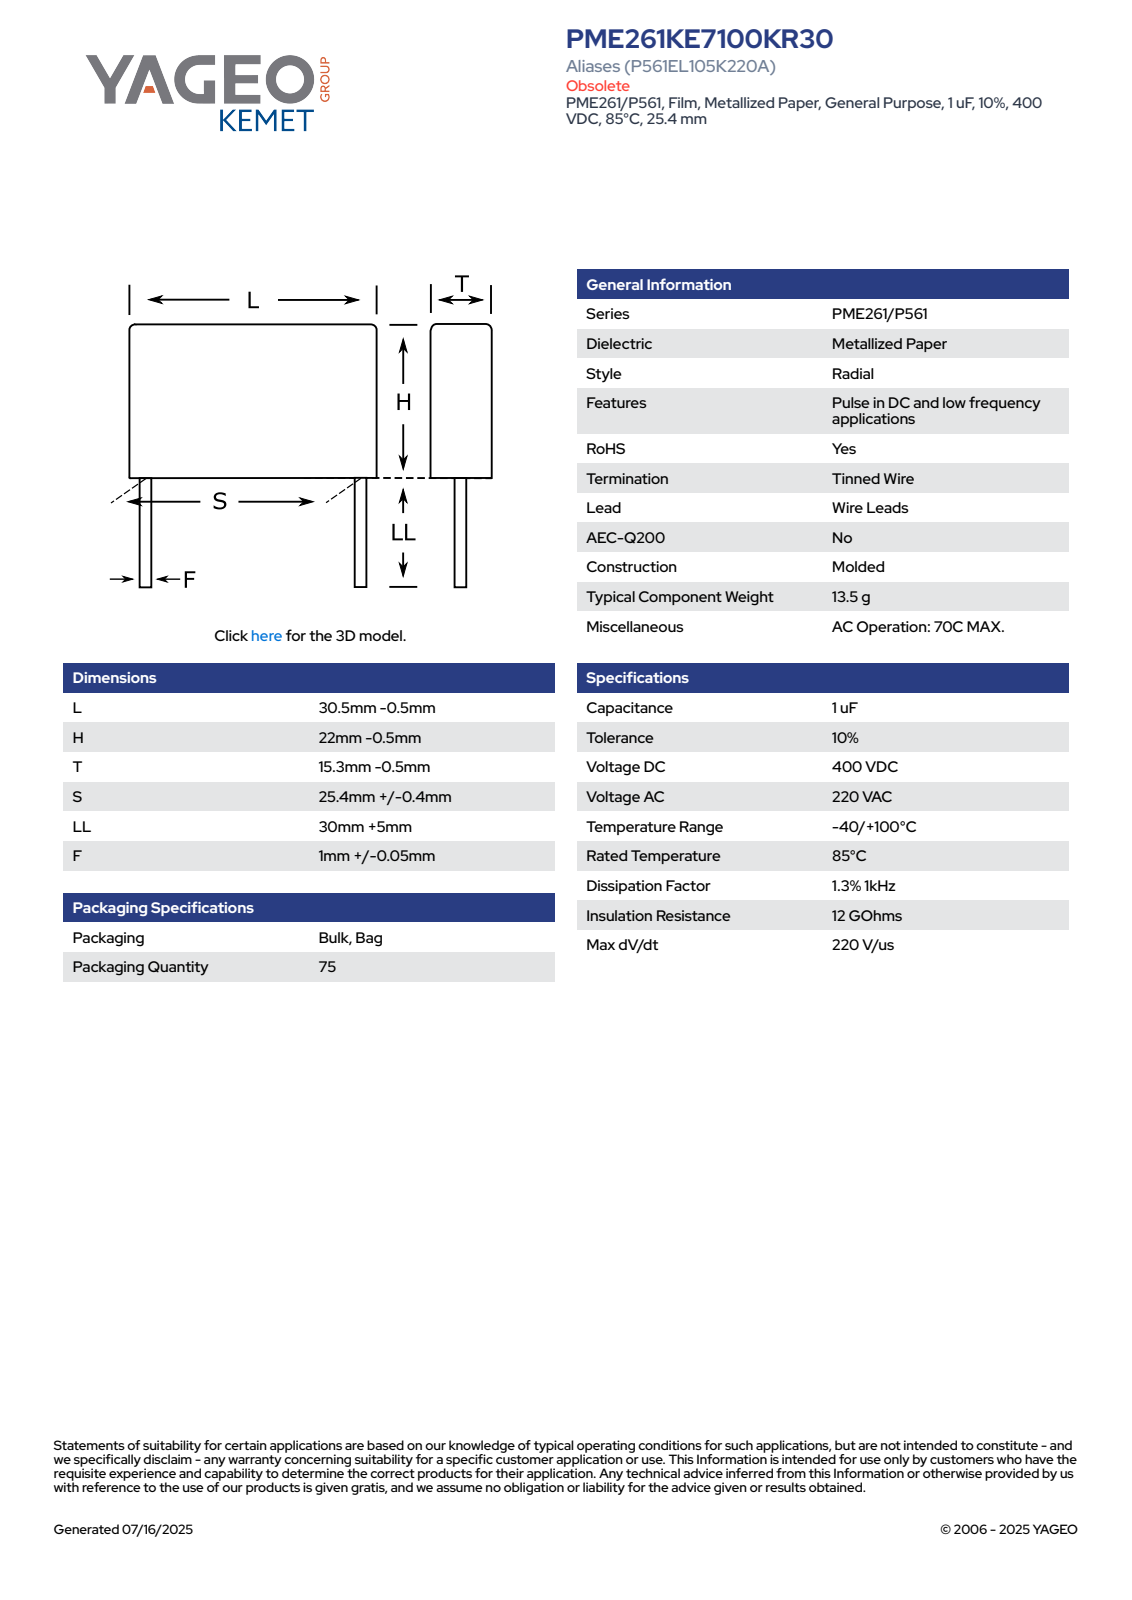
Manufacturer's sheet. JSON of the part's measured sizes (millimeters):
{"part_name": "CFR_MOLDED_30.5X22X15.3_L30H21.5T14.8S25.4LL35F1.05", "step_written_by": "SolidWorks 2021 (AUTOMOTIVE_DESIGN)", "units": "millimeters", "bodies": {"solids": 4, "faces": 73, "planar": 65, "cylindrical": 8, "other": 0}, "overall_size": [56.5, 30, 14.8], "volume_mm3": 9602, "surface_area_mm2": 3069, "round_bosses_or_shafts": [[1.05, 2]], "partial_cylinders_radius": [[0.5, 4]], "face_to_face_distances": [14.8, 21.5, 30, 35, 56.5, 46.7, 11.7, 9.8, 44.01, 9.01]}
